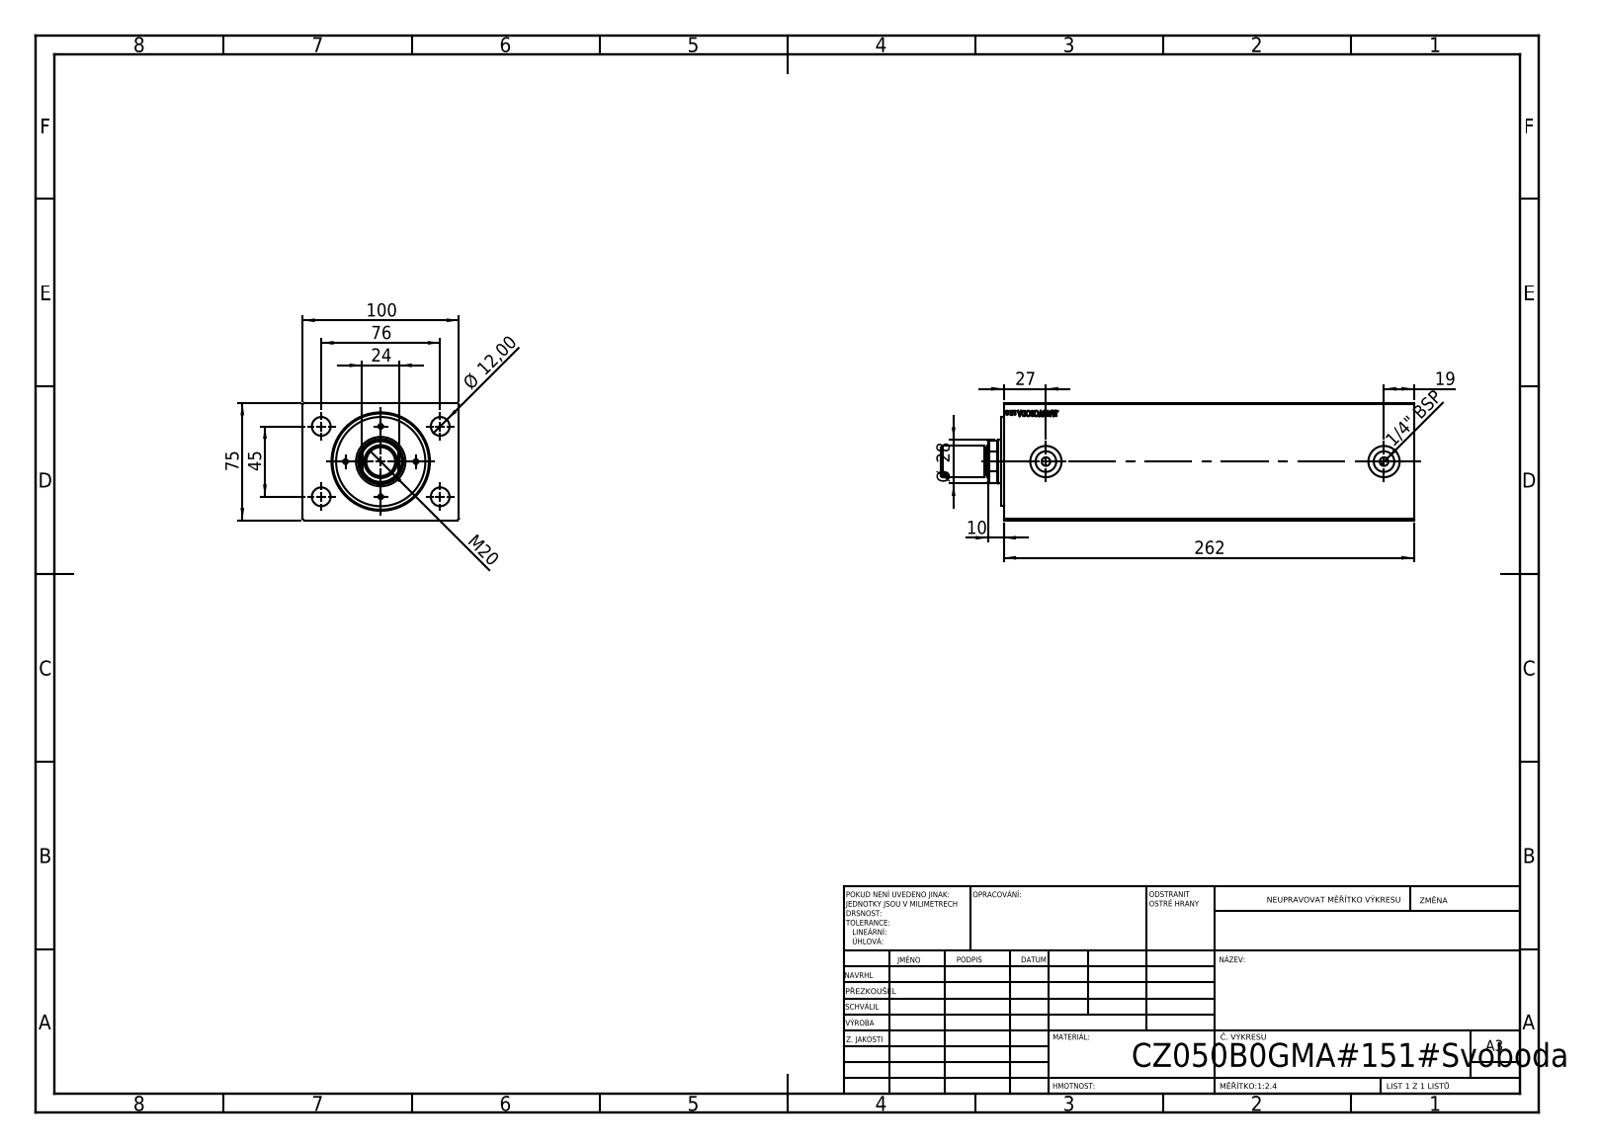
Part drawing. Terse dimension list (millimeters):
name: V500CZ; V500CZ_MALE_METRIC; V500CZ_B_VC
written by: SolidWorks 2019 (CONFIG_CONTROL_DESIGN)
unit: mm
bodies: 4 solids, 888 faces (404 planar, 62 cylindrical, 422 other)
size: 302 × 100 × 75
volume: 1 700 000 mm³; area: 195 477 mm²
holes: 4× ⌀3, 4× ⌀12, 2× ⌀5.5, 2× ⌀13.16, 2× ⌀20, 1× ⌀18.5, 1× ⌀28, 1× ⌀29, 1× ⌀36, 1× ⌀50, 1× ⌀61.5
bosses: 1× ⌀57, 1× ⌀20, 1× ⌀18
rounds: 1× R13.5
face distances: 75, 100, 262, 244.2, 17.8, 10, 8.2, 1.8, 236, 253.8
hole spacings: 22.5, 27.32, 31.82, 38, 44.16, 45, 58.9, 64.55
